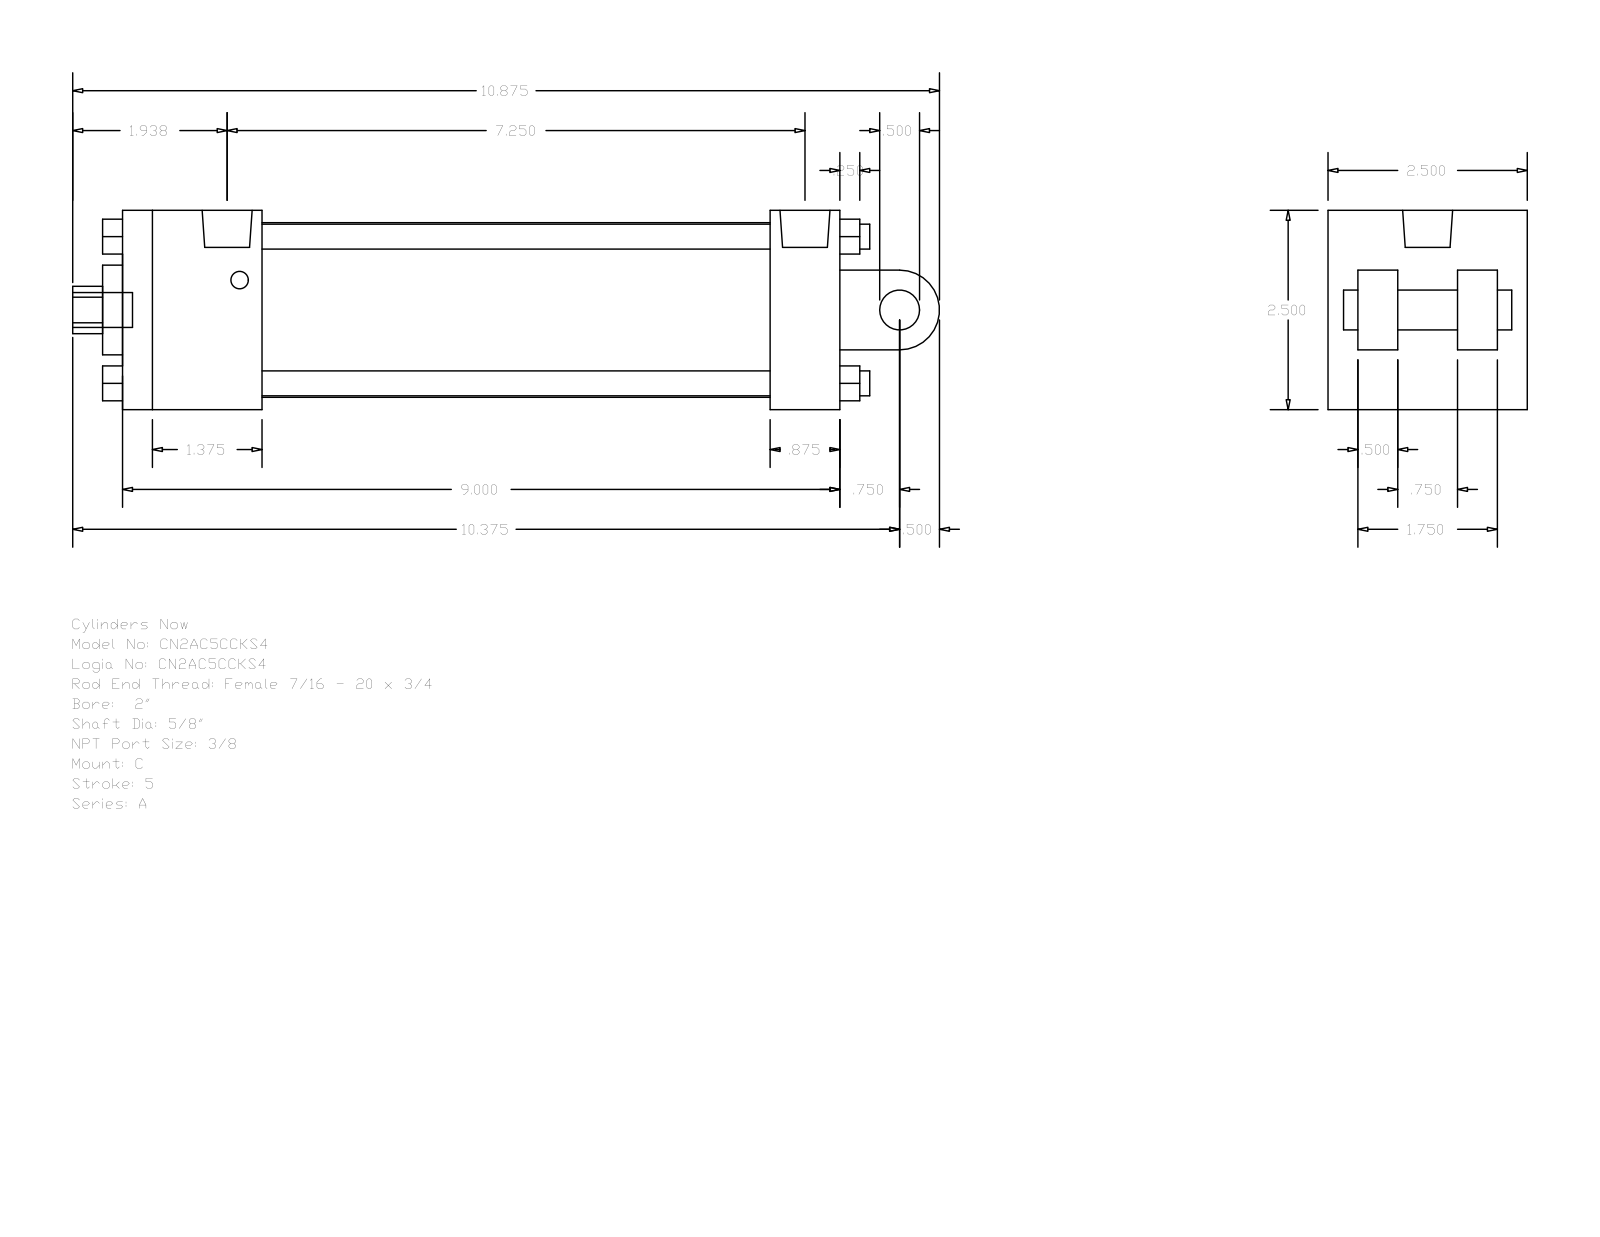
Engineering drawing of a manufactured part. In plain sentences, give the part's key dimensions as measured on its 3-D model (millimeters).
The part is named "A_C__0200_0.625". Its 3-D file was written by "GSSL Pune (CONFIG_CONTROL_DESIGN)". It is 0 solids with 135 faces: 102 planar, 33 cylindrical and 0 other. Overall it measures 276.23 by 63.5 by 63.5 millimeters. Round holes: 2 of diameter 5.56, 1 of diameter 15.88, 1 of diameter 15.93, 1 of diameter 28.57, 1 of diameter 55.63. Round bosses or shafts: 4 of diameter 7.94, 2 of diameter 5.56, 1 of diameter 15.93, 1 of diameter 12.7, 1 of diameter 11.11. Partial cylindrical surfaces (rounded edges, fillets, slot ends): 1 of radius 7.54, 1 of radius 12.7. The main face-to-face distances are 63.5, 228.59, 22.22, 44.45, 184.14, 206.37, 161.92, 12.7, 41.28, 9.52. The hole center spacings are 3.97.
